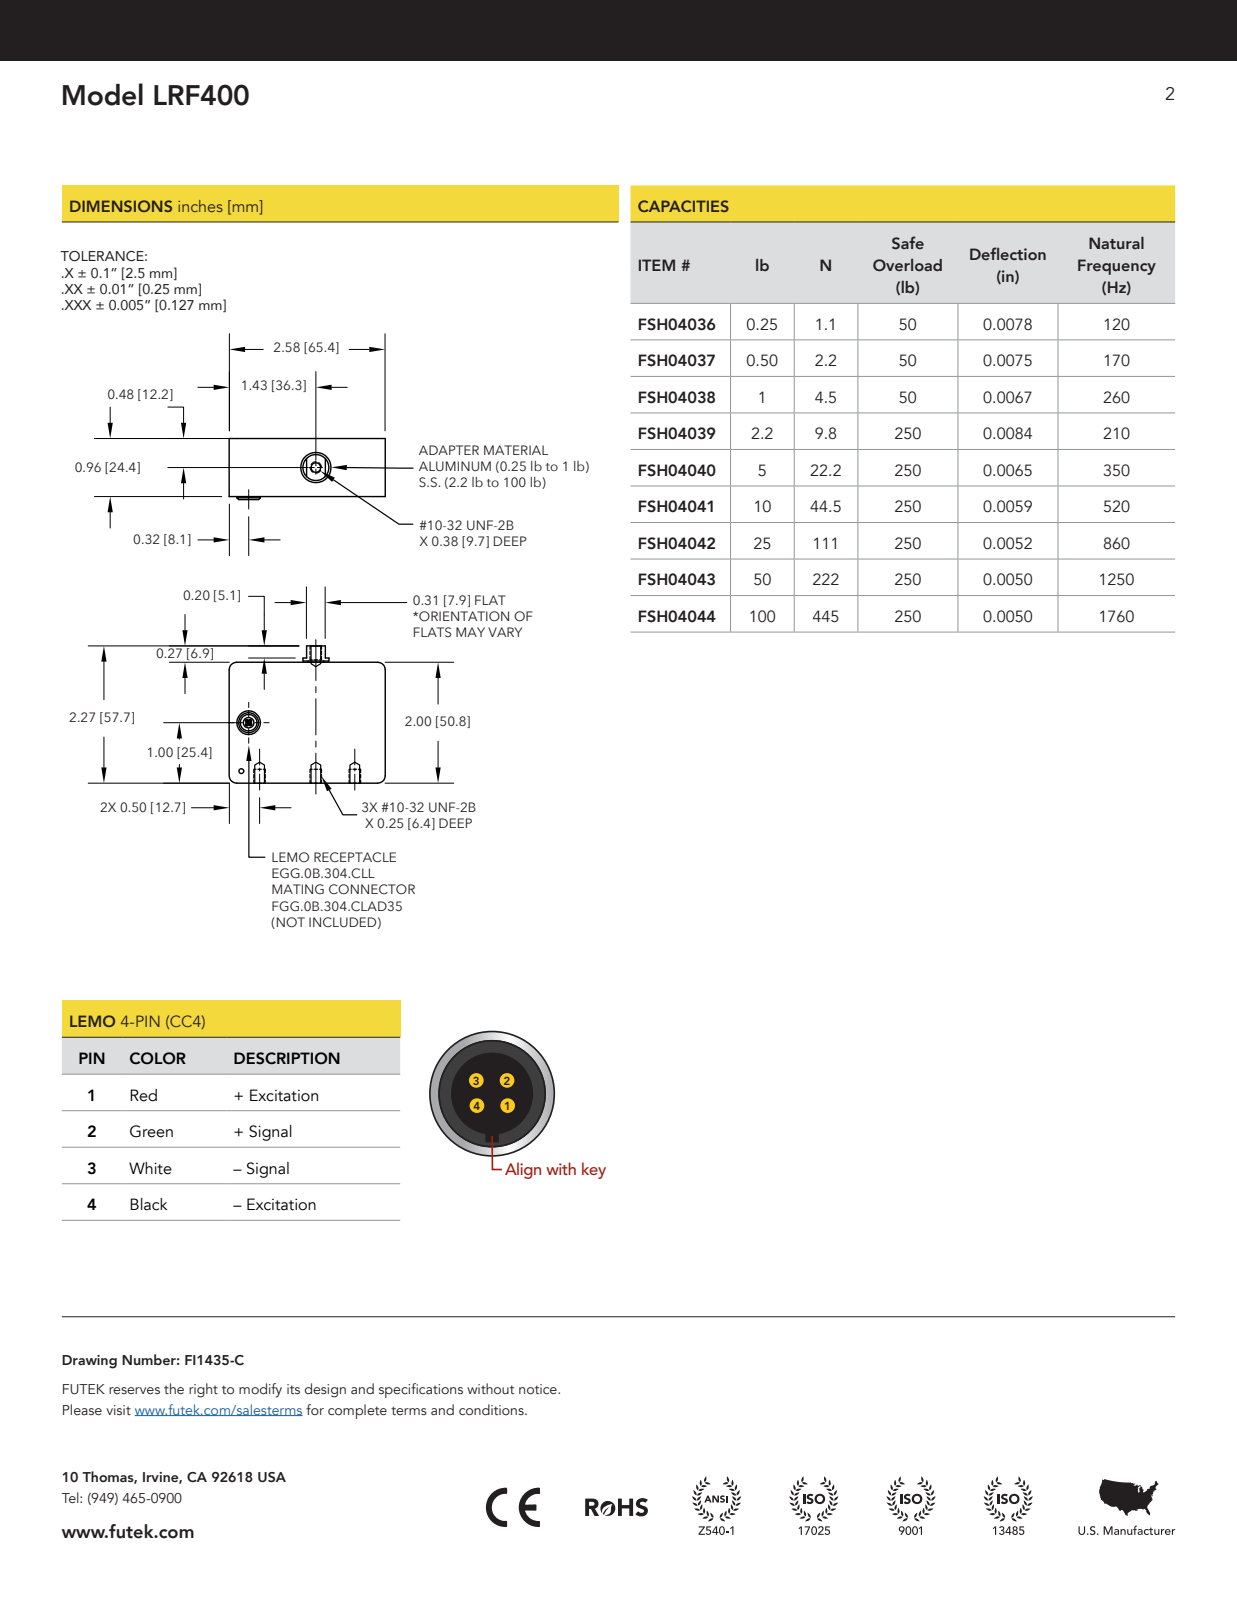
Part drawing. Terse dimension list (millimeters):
name: LRF400 Lemo; ~$F1649-B
written by: Autodesk Inventor 2008 (AUTOMOTIVE_DESIGN)
unit: mm
bodies: 1 solid, 85 faces (42 planar, 37 cylindrical, 6 other)
size: 65.4 × 57.7 × 25.7
volume: 79 220 mm³; area: 14 350 mm²
holes: 4× ⌀0.7, 4× ⌀1.3, 3× ⌀4.1, 1× ⌀2.1, 1× ⌀7, 1× ⌀8.4, 1× ⌀9.5, 1× ⌀12.7
bosses: 4× ⌀1, 1× ⌀10.9, 1× ⌀9.9, 1× ⌀6.4, 1× ⌀4.6, 1× ⌀4.4
rounds: 11× R3.2
face distances: 24.1, 50.8, 65.4, 24.4, 1, 0.5, 1.5, 1.5, 6.4, 2
hole spacings: 1.5, 1, 2.1, 1.1, 16.4, 19.7, 20, 20.5
